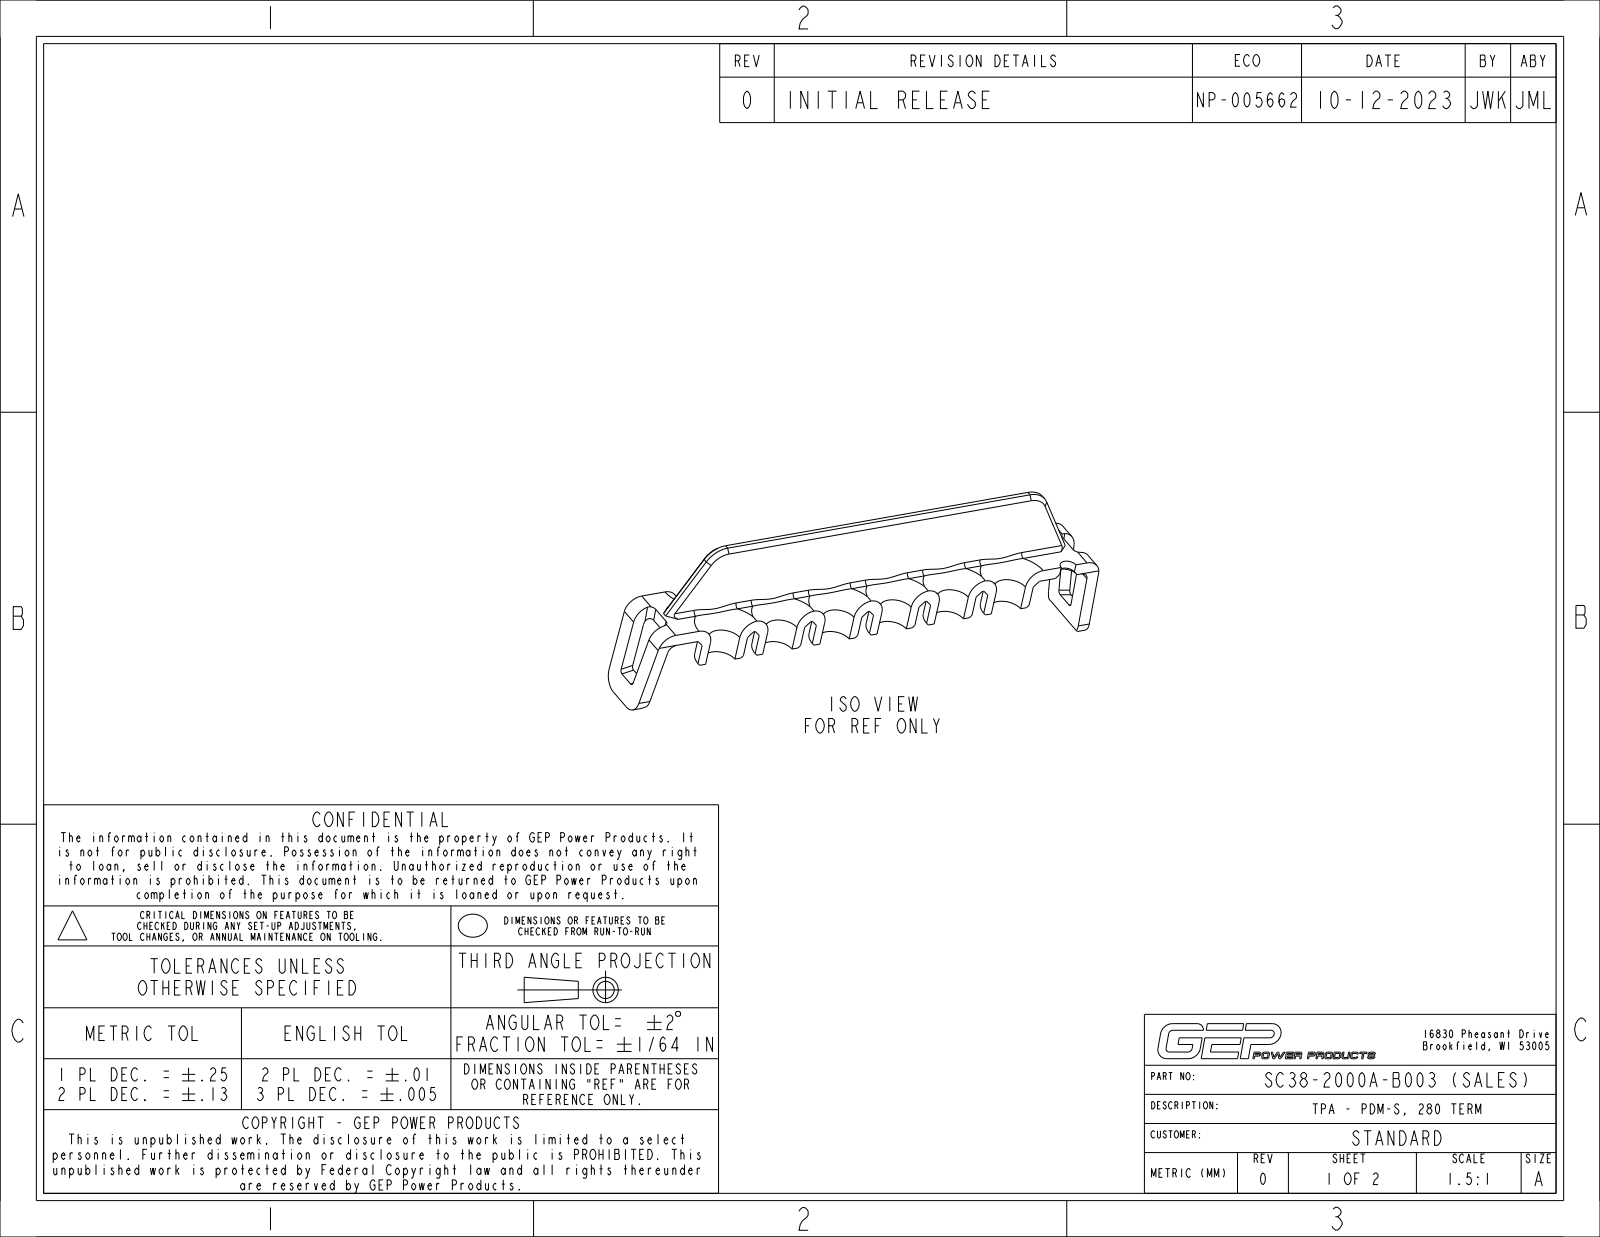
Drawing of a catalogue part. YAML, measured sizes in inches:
part_name: "PC38-2000A-B003_NCF; SC38-2000A-B003_NCF_ASM"
step_written_by: "CREO PARAMETRIC BY PTC INC, 2017110 (CONFIG_CONTROL_DESIGN)"
units: inches
bodies: {solids: 1, faces: 223, planar: 107, cylindrical: 62, other: 54}
overall_size: [2.433, 0.787, 0.319]
volume: 0.102
surface_area: 4.334
round_bosses_or_shafts:
  - {diameter: 0.118, count: 1}
partial_cylinders:
  - {radius: 0.079, count: 16}
  - {radius: 0.122, count: 12}
  - {radius: 0.016, count: 4}
  - {radius: 0.028, count: 4}
  - {radius: 0.039, count: 4}
  - {radius: 0.02, count: 2}
  - {radius: 0.118, count: 2}
face_to_face_distances: [0.059, 0.13, 0.189, 0.319, 0.142, 0.201, 0.087, 0.394, 0.535, 0.335]
